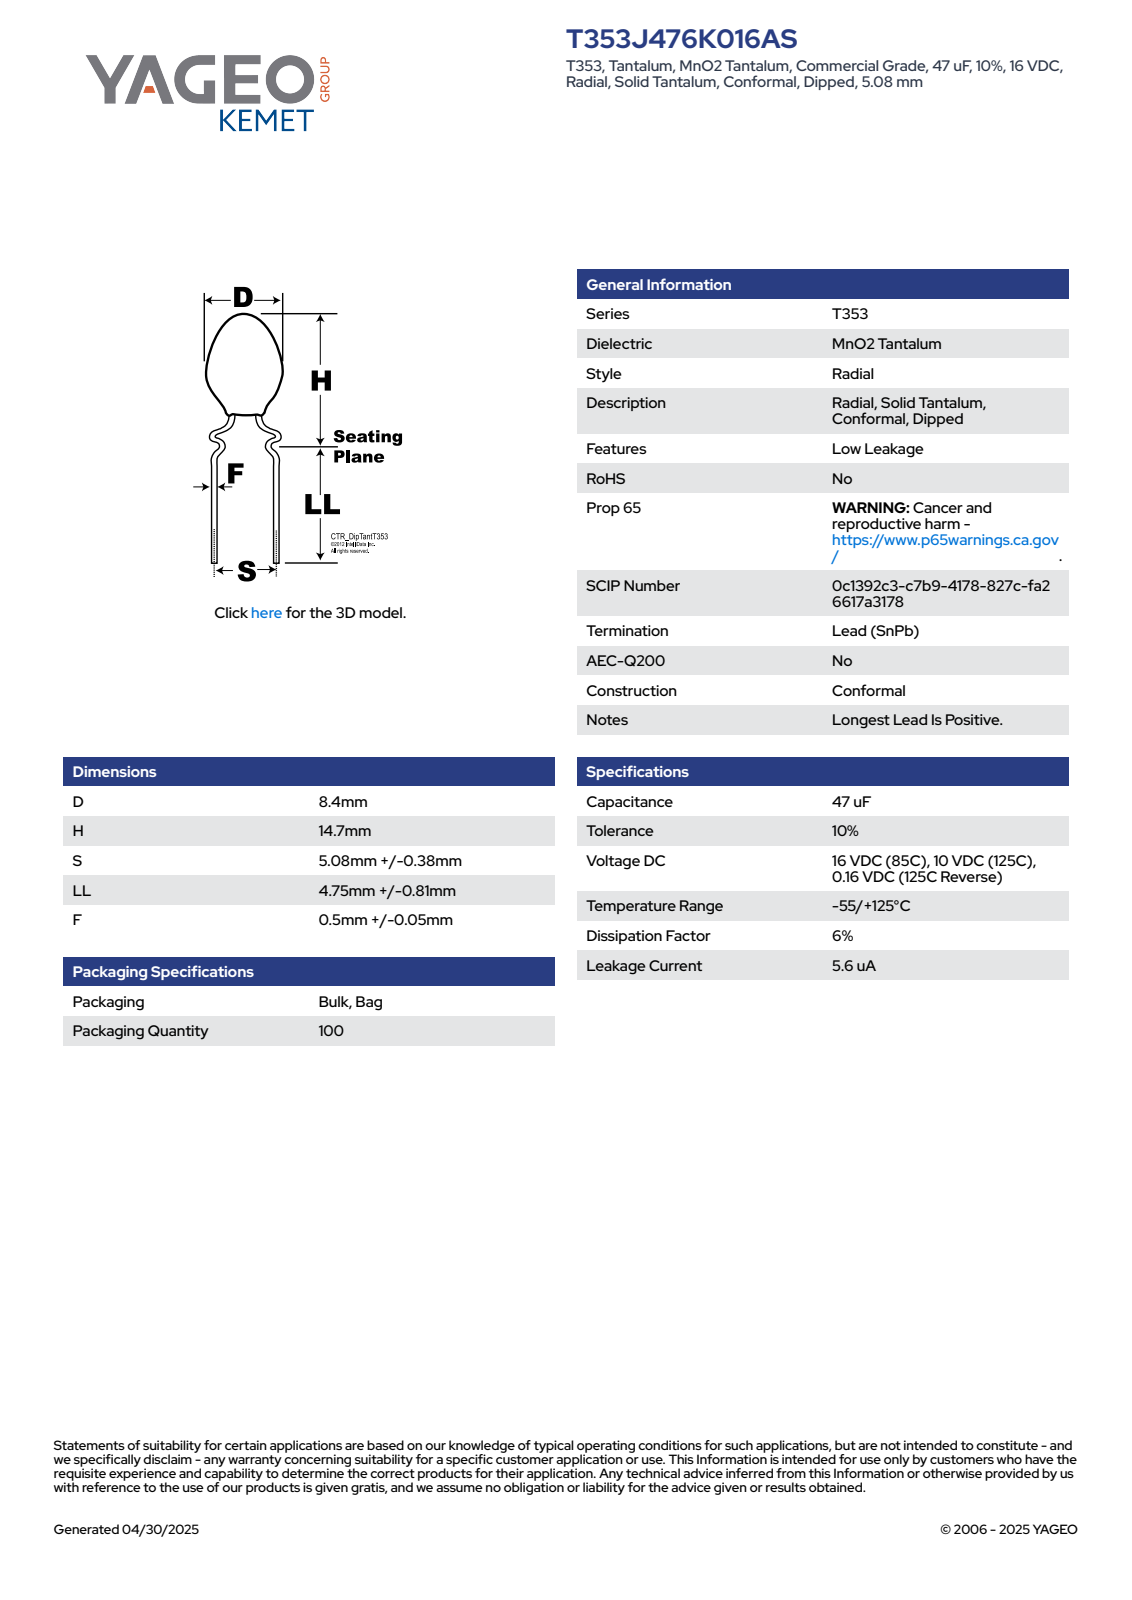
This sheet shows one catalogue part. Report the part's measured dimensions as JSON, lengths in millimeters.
{"part_name": "CTR_T353_D8.4H14.7S5.08LL5.56F0.55", "step_written_by": "SolidWorks 2014 (AUTOMOTIVE_DESIGN)", "units": "millimeters", "bodies": {"solids": 1, "faces": 89, "planar": 29, "cylindrical": 10, "other": 50}, "overall_size": [20.26, 8.4, 8.4], "volume_mm3": 464, "surface_area_mm2": 334, "round_bosses_or_shafts": [[0.55, 2], [8.4, 1]], "partial_cylinders_radius": [[4.19, 1]], "face_to_face_distances": [10.09, 10.17, 20.26, 4.64, 5.45, 15.82, 5.65, 4.44, 14.81, 1.01]}
